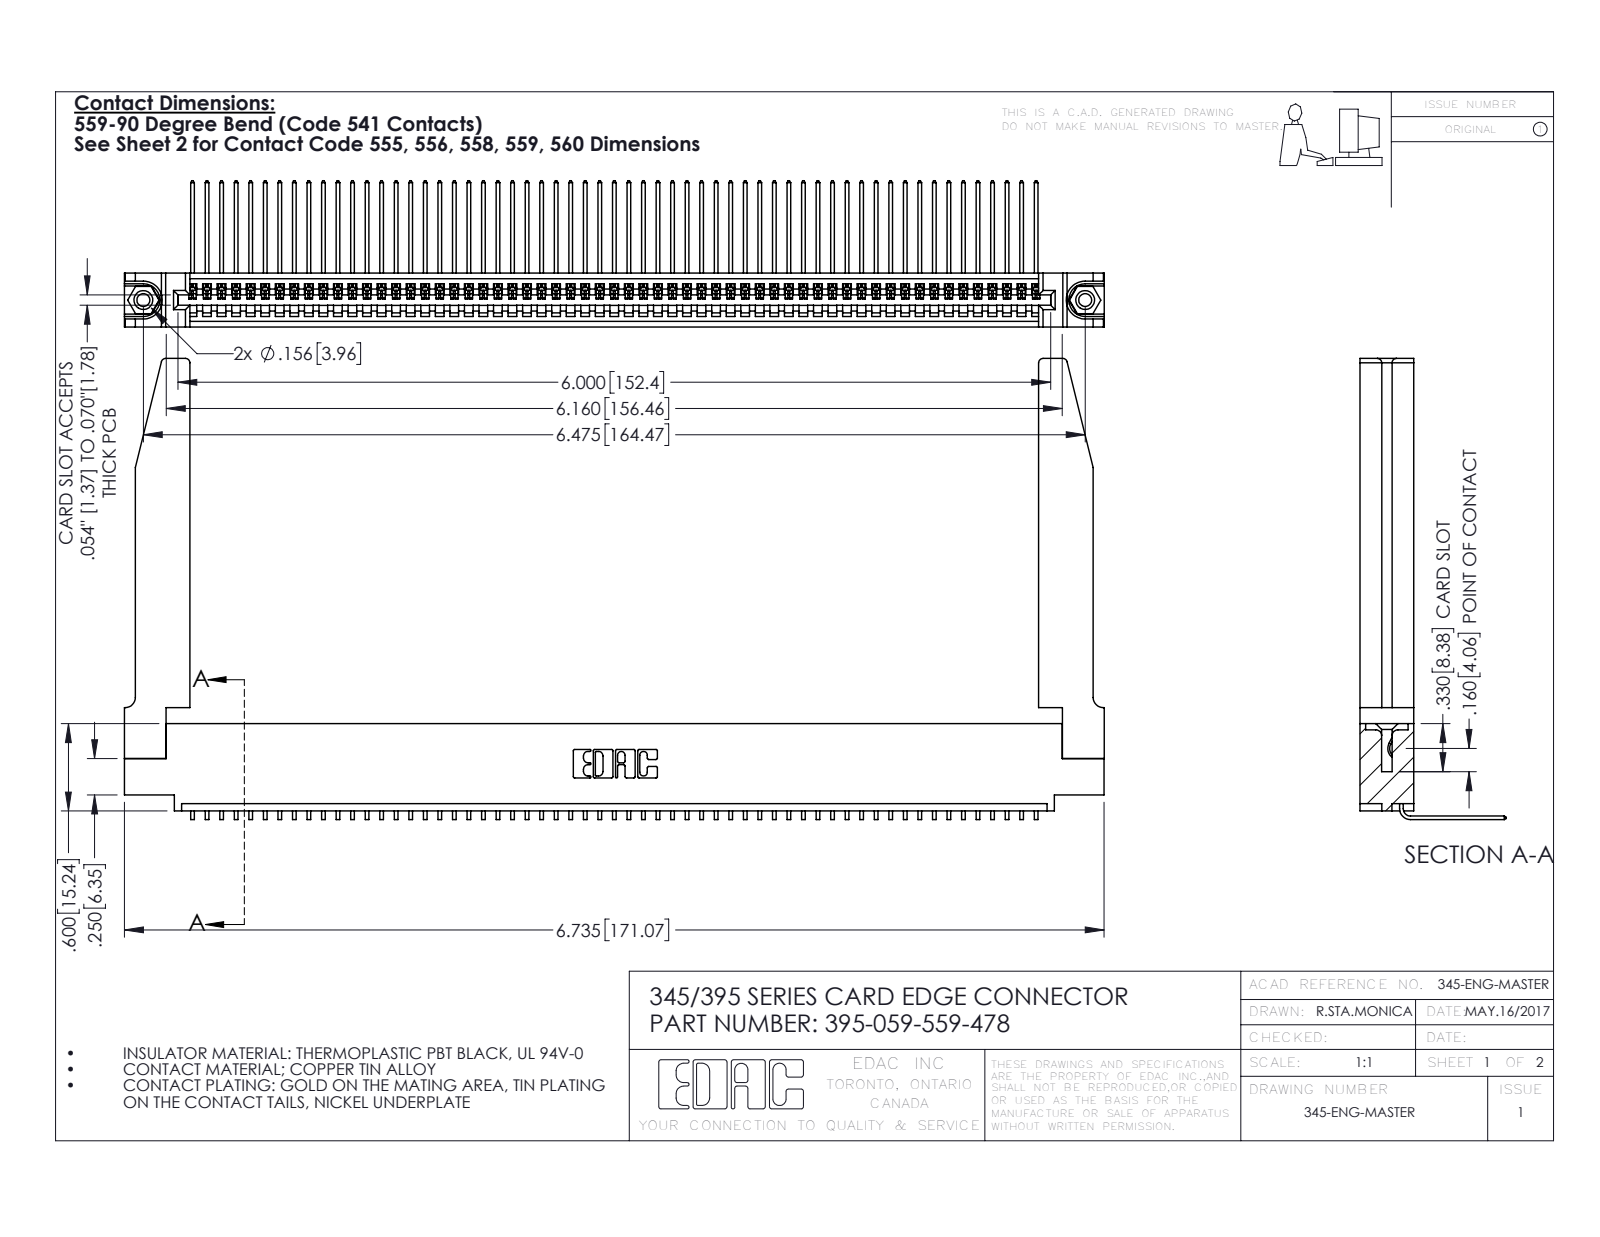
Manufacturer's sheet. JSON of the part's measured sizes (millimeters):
{"part_name": "345-292-001_558 559 Tail - 1; 345-220-078_345-220-078; 345-250-001_345-250-001-102; 395-059-559-478 (+1 more)", "step_written_by": "SolidWorks 2016 (CONFIG_CONTROL_DESIGN)", "units": "millimeters", "bodies": {"solids": 64, "faces": 3904, "planar": 2704, "cylindrical": 1148, "other": 52}, "overall_size": [171.1, 80.5, 25.5], "volume_mm3": 24290, "surface_area_mm2": 30260, "round_holes": [[2.3, 2], [3.2, 2], [4, 2], [1.6, 1]], "round_bosses_or_shafts": [[3.9, 2]], "partial_cylinders_radius": [[0.2, 118], [0.3, 22], [0.8, 8], [0.2, 6], [0.8, 6], [0.7, 3], [0.8, 2], [1, 2]], "face_to_face_distances": [9.4, 1.8, 7.6, 2.5, 6.9, 0.6, 5.1, 5.7, 3.8, 3.8], "hole_center_spacings": [6.9, 158.5, 164.5]}
